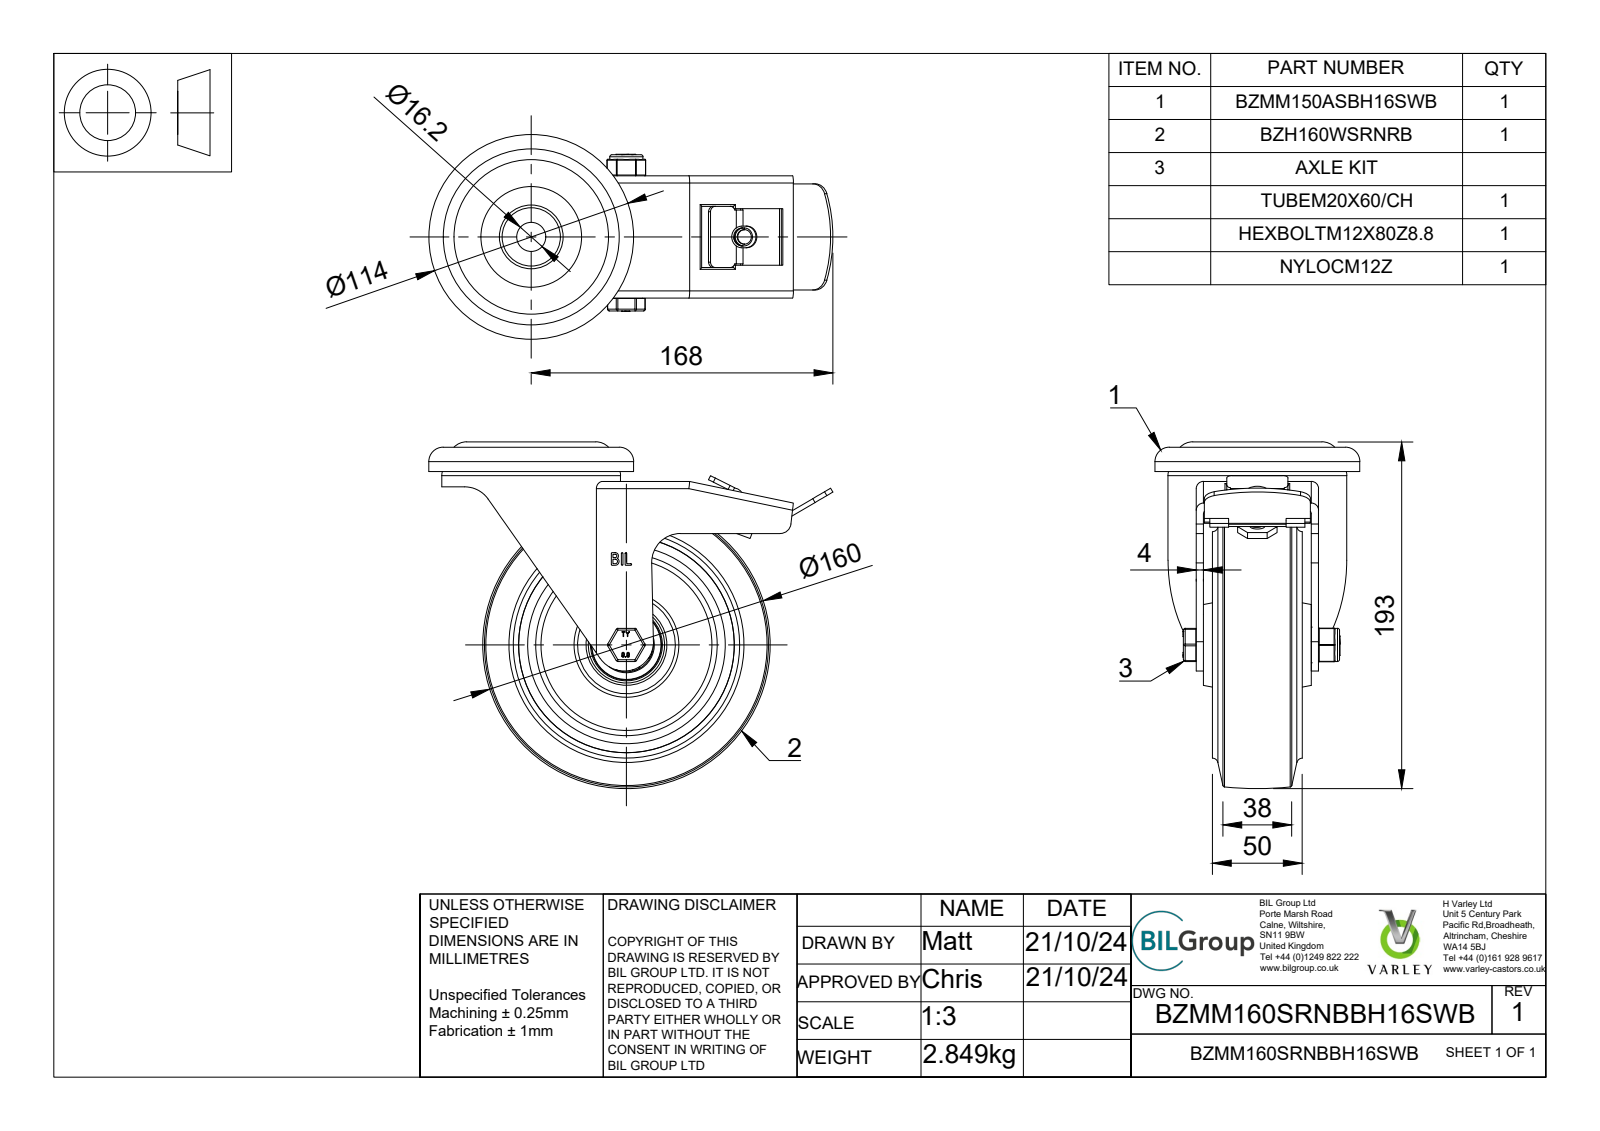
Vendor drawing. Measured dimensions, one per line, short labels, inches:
name: BZMM160SRNBBH16SWB v3; BZMM150ASBH16SWB v1; ZINC PLATED, PRESSED STEEL HEAD; ZINC PLATED, PRESSED STEEL FORKS (+8 more)
written by: Autodesk Translation Framework v13.20.0.188 (AUTOMOTIVE_DESIGN)
unit: in
bodies: 21 solids, 620 faces (321 planar, 189 cylindrical, 110 other)
size: 8.858 × 7.598 × 4.488
volume: 54.23 in³; area: 428.7 in²
holes: 1× ⌀0.394, 1× ⌀0.404, 1× ⌀0.472, 1× ⌀0.48, 1× ⌀0.492, 1× ⌀0.551, 1× ⌀0.638, 1× ⌀0.787, 1× ⌀1.181, 1× ⌀1.575, 1× ⌀1.614, 1× ⌀2.028
bosses: 8× ⌀0.197, 1× ⌀4.488, 1× ⌀3.917, 1× ⌀2.913, 1× ⌀1.85, 1× ⌀1.28, 1× ⌀0.783, 1× ⌀0.728
rounds: 22× R0.02, 18× R0.039, 8× R0.079, 4× R0.118, 4× R0.157, 3× R0.236, 3× R0.315, 2× R0.63
face distances: 0.157, 1.063, 1.299, 0.197, 0.866, 0.039, 2.165, 1.102, 0.098, 0.236
